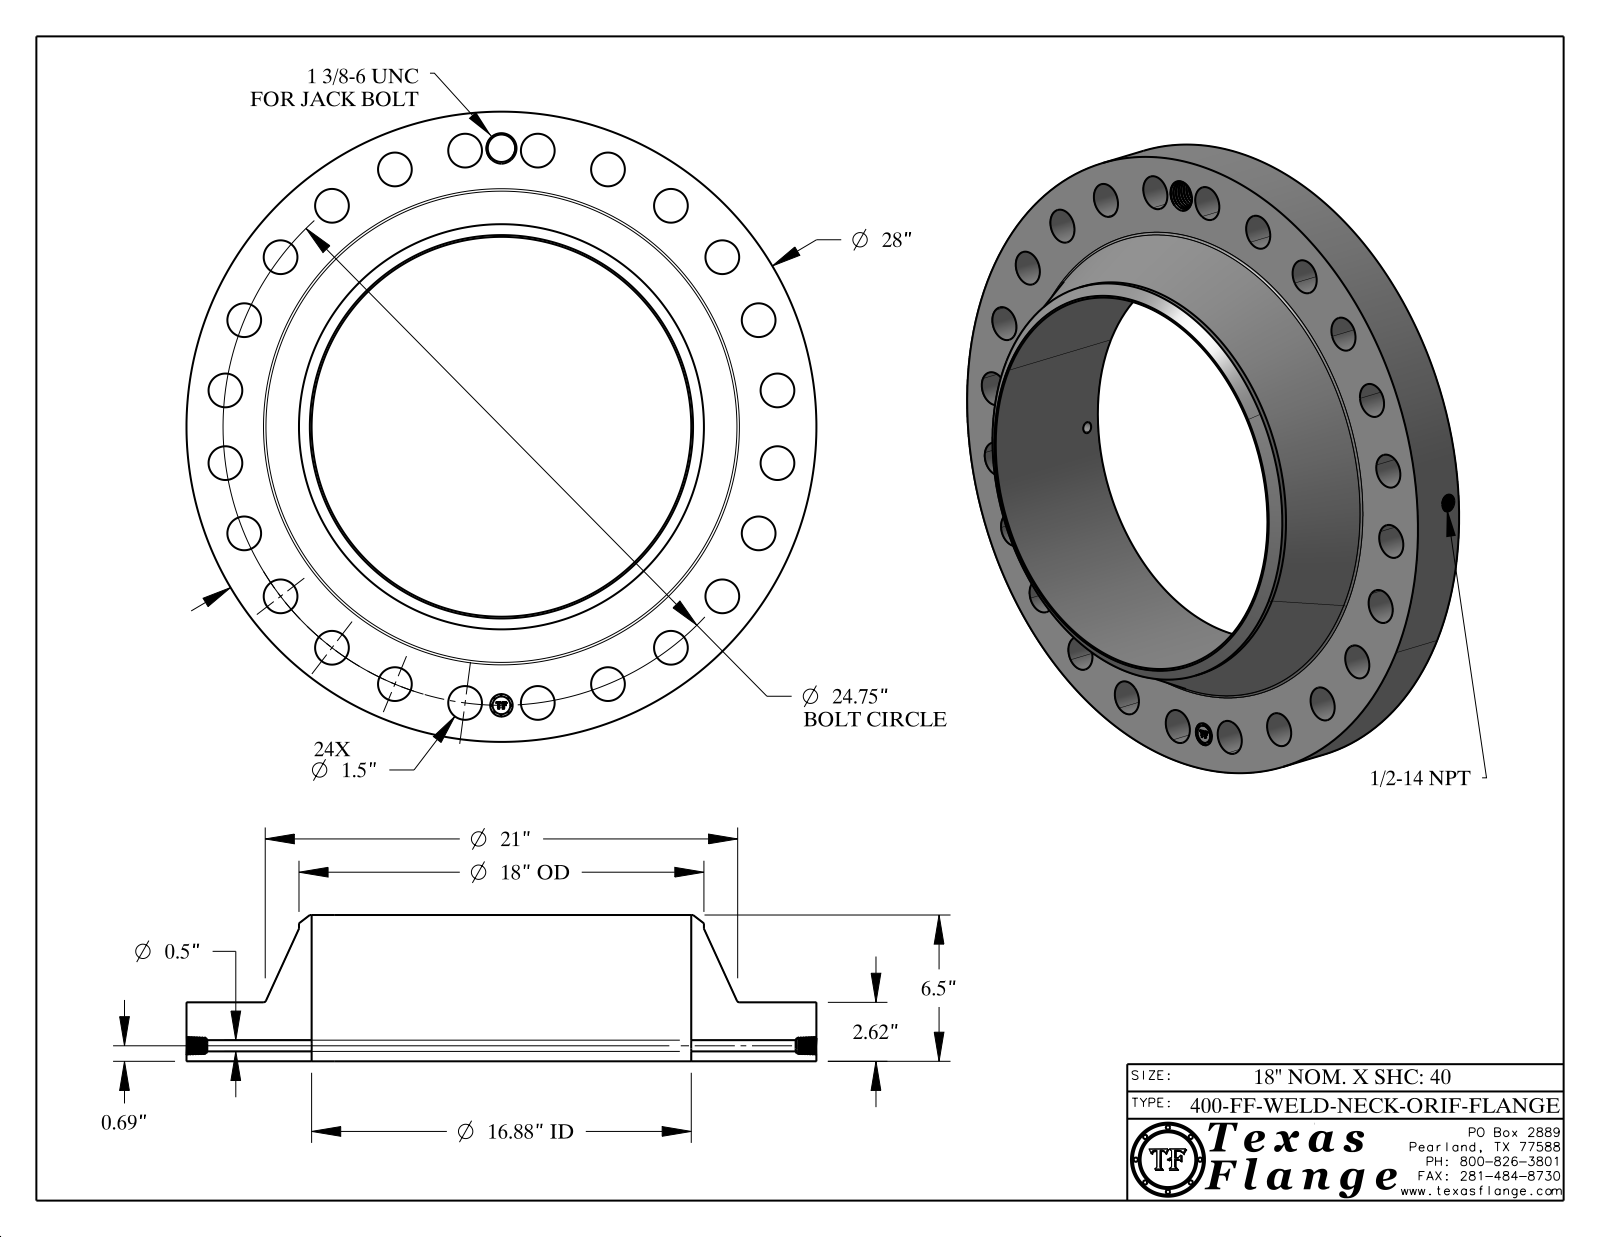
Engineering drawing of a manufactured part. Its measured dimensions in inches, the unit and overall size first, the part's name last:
Units: inches
Overall size (bounding box): 28 × 28 × 6.5
Round holes (diameter × count): ⌀1.5 ×24, ⌀0.5 ×1, ⌀0.672 ×1, ⌀1 ×1, ⌀1.219 ×1, ⌀16.876 ×1
Round bosses / shafts (diameter × count): ⌀0.061 ×8, ⌀28 ×1, ⌀18 ×1, ⌀0.788 ×1
Main face-to-face distances: 2.62, 6.5, 3.88, 0.015, 2.605, 3.895, 0.298, 0.292, 0.054, 0.248
Hole centre spacings: 12.375, 15.067, 21.434, 22.866, 23.907, 6.406, 17.501, 3.23
Volume: 1 171 in³ · Surface area: 1 751 in²
Bodies: 1 solid, 803 faces (368 planar, 125 cylindrical, 310 other)
Part name (STEP PRODUCT): 400-FF-WELD-NECK
STEP written by: CATIA V5 STEP AP214 (AUTOMOTIVE_DESIGN)
